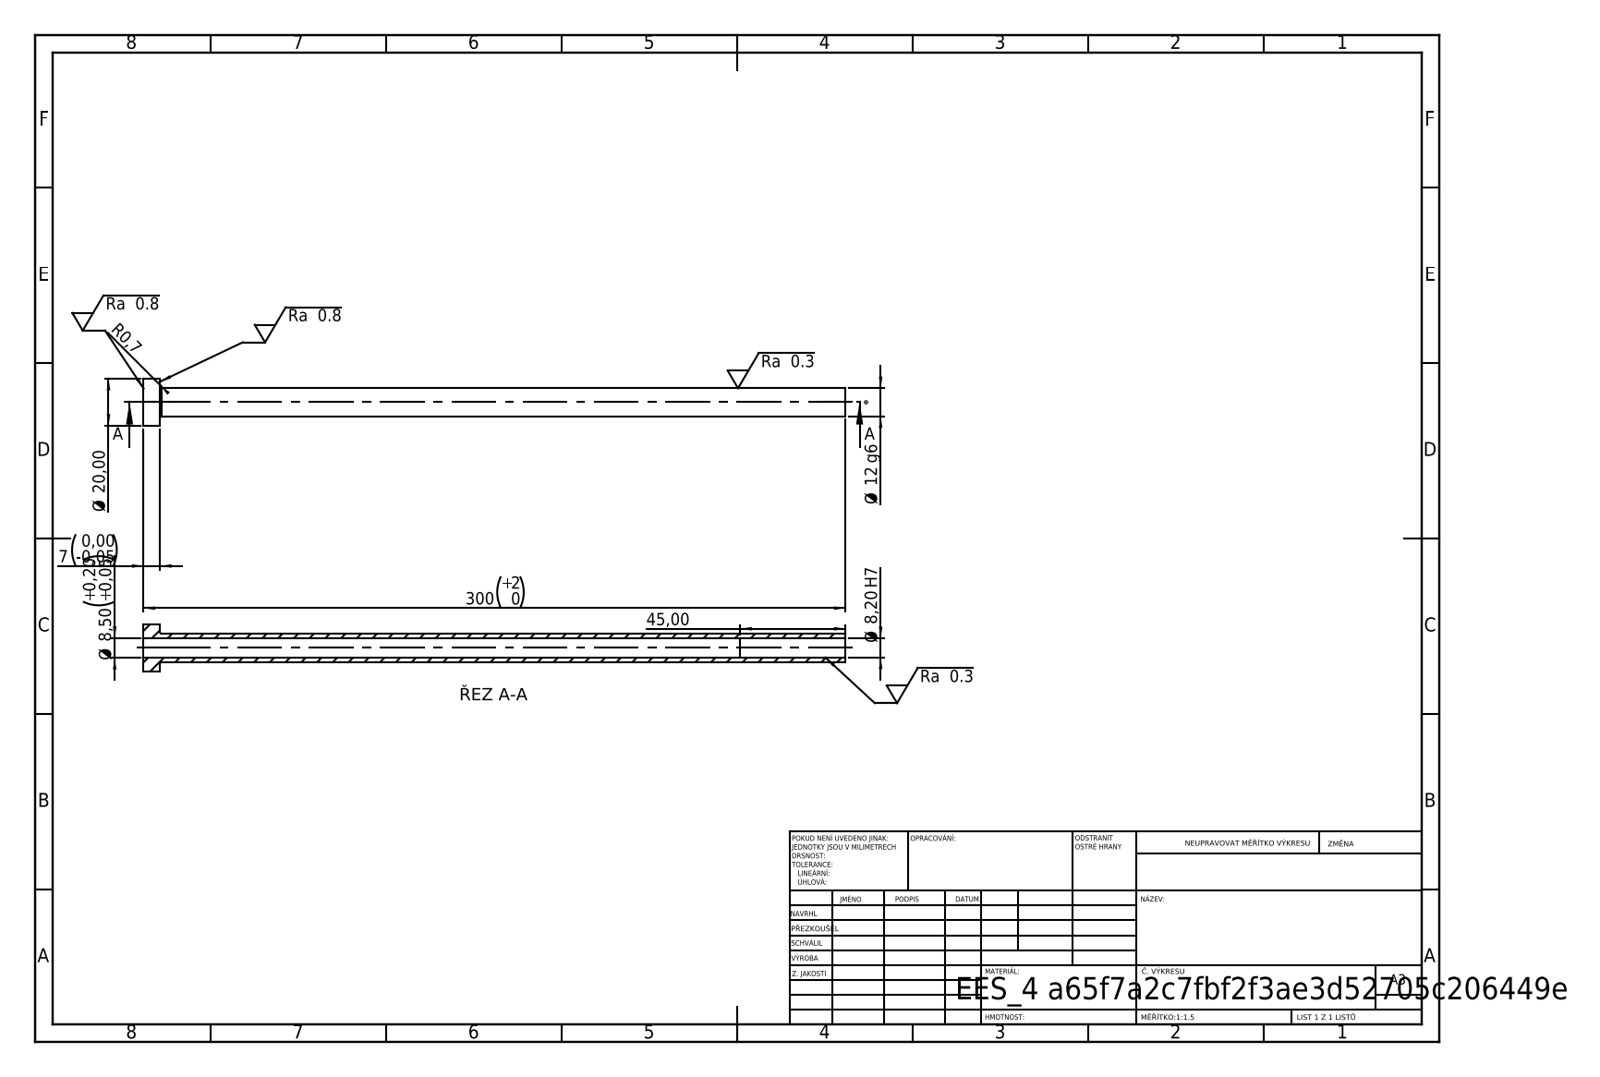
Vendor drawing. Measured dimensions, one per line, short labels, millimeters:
written by: SolidWorks 2019 (CONFIG_CONTROL_DESIGN)
unit: mm
bodies: 1 solid, 14 faces (4 planar, 8 cylindrical, 2 other)
size: 300 × 20 × 20
volume: 18 494 mm³; area: 19 966 mm²
holes: 1× ⌀8.2, 1× ⌀8.5
bosses: 1× ⌀20, 1× ⌀12
face distances: 7, 300, 293, 255, 248, 45
